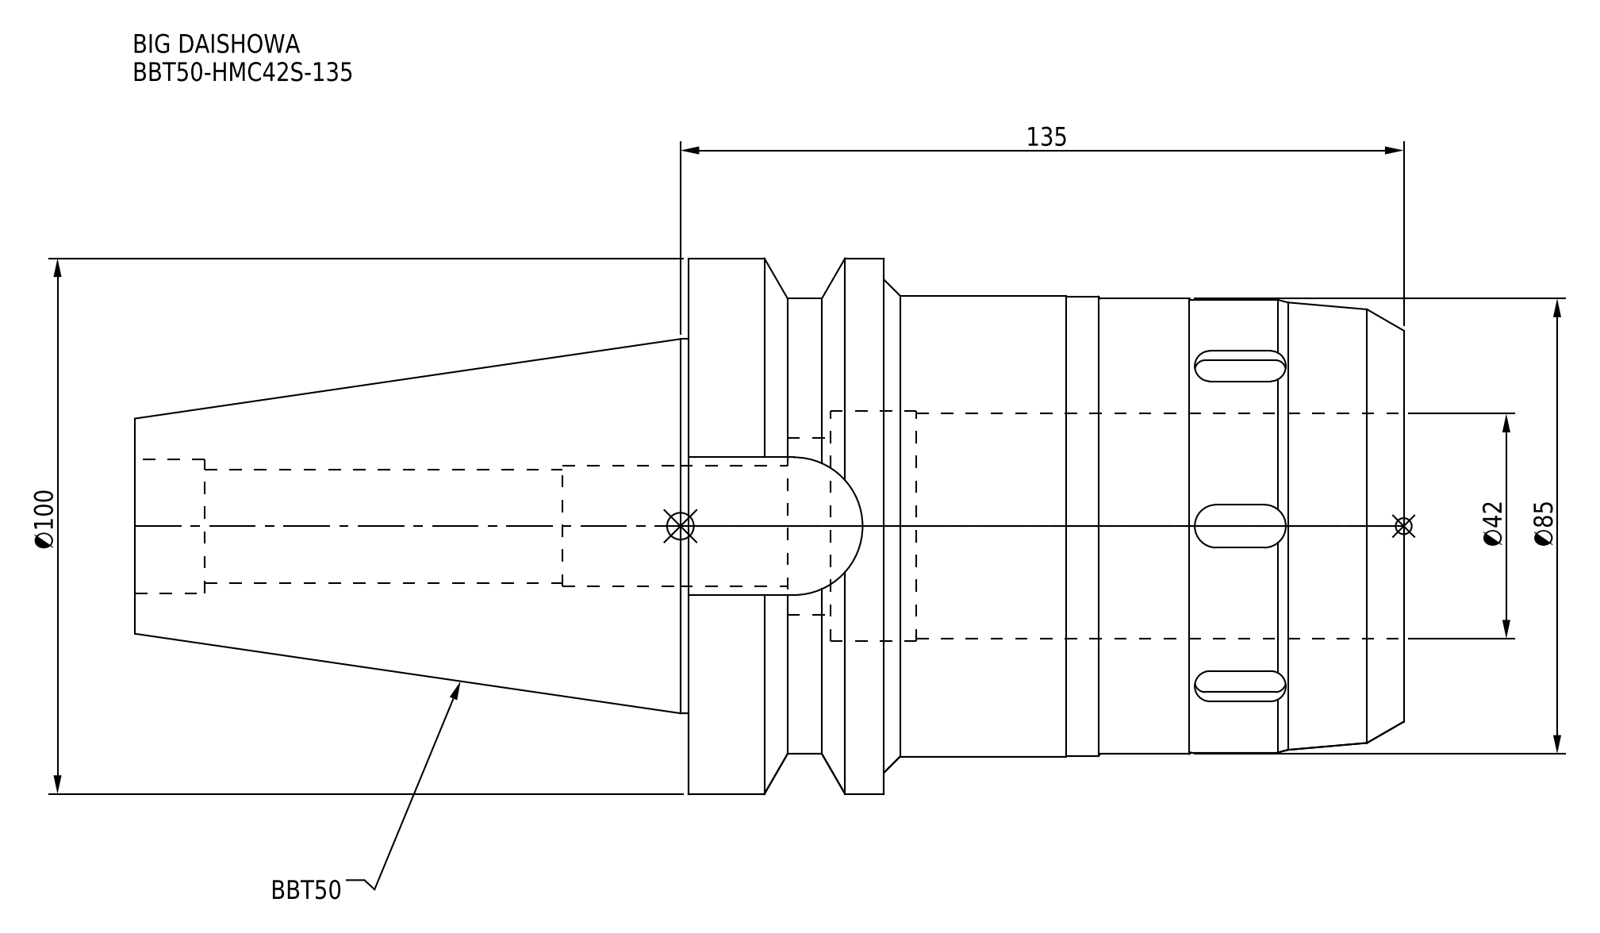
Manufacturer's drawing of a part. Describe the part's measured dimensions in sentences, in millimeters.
The part is named "BBT50-HMC42S-135". Its 3-D file was written by "CREO PARAMETRIC BY PTC INC, 2016380 (AUTOMOTIVE_DESIGN)". It is 1 solid with 104 faces: 40 planar, 46 cylindrical and 18 other. Overall it measures 236.8 by 100 by 100 millimeters. Its volume is 837 097 cubic millimeters and its surface area 92 928 square millimeters. Round holes: 1 of diameter 21.2, 1 of diameter 22.5, 1 of diameter 25, 1 of diameter 33, 1 of diameter 42, 1 of diameter 43. Round bosses or shafts: 1 of diameter 100, 1 of diameter 86, 1 of diameter 85.7, 1 of diameter 85, 1 of diameter 84.5, 1 of diameter 69.85. Partial cylindrical surfaces (rounded edges, fillets, slot ends): 12 of radius 4, 1 of radius 12.85. The main face-to-face distances are 133.5, 97, 36.5, 236.8, 139.8, 103.3, 70.8, 8, 107, 10.
